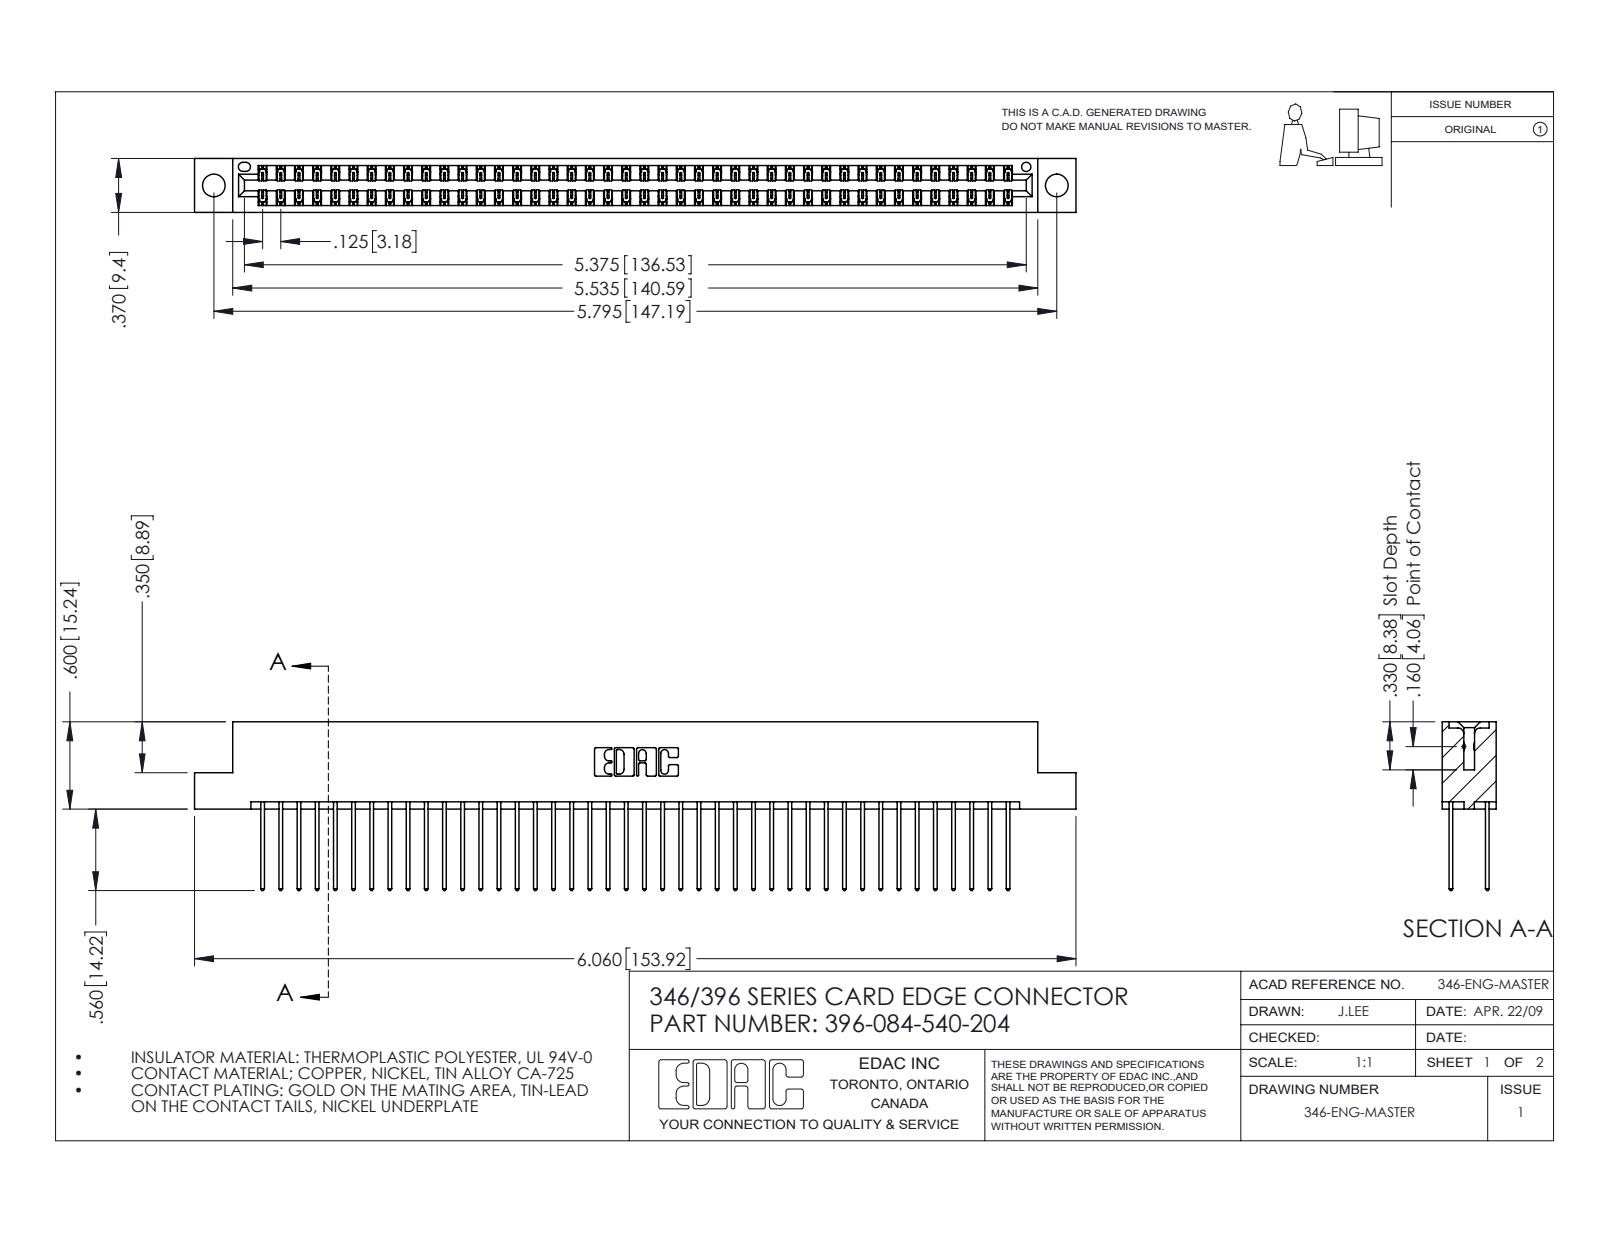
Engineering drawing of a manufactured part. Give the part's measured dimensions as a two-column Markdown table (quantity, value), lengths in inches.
| quantity | value |
| --- | --- |
| part name | 345-292-001_345-293-140; 396-084-540-204; 346 Part_Flush Mounting Lugs - 0.156 Dia-TH |
| STEP written by | SolidWorks 2016 (CONFIG_CONTROL_DESIGN) |
| units | inches |
| bodies | 85 solids, 4490 faces (3016 planar, 1474 cylindrical, 0 other) |
| overall size | 6.06 × 1.16 × 0.37 |
| volume | 0.93 in³ |
| surface area | 34.52 in² |
| round holes (diameter × count) | 0.156 × 2, 0.064 × 1 |
| partial cylindrical surfaces (radius × count) | 0.006 × 126, 0.01 × 84, 0.01 × 22, 0.007 × 6, 0.031 × 6, 0.026 × 3, 0.014 × 2, 0.022 × 2 |
| main face-to-face distances | 0.048, 0.322, 0.25, 0.072, 0.298, 0.025, 0.37, 0.275, 0.148, 0.222 |
| hole center spacings | 0.246, 5.586, 5.795 |
